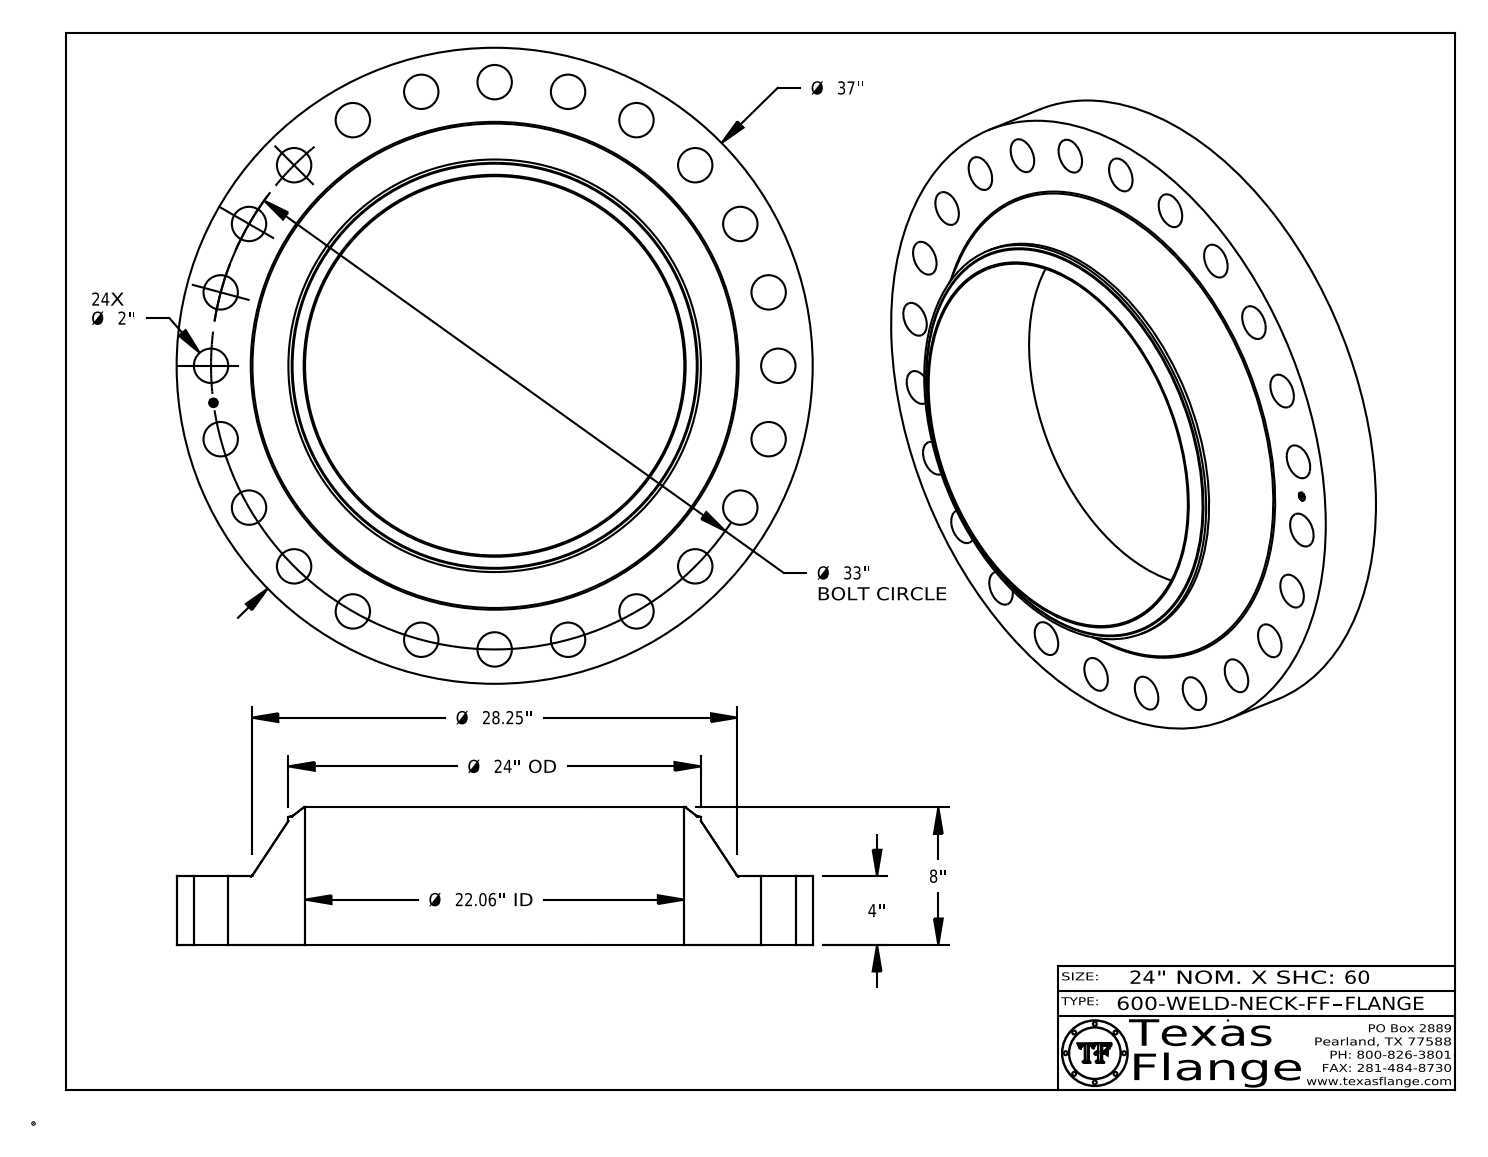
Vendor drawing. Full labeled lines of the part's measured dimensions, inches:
Part name (STEP PRODUCT): 600-WELD-NECK-FF
STEP written by: CATIA V5 STEP AP214 (AUTOMOTIVE_DESIGN)
Units: inches
Bodies: 1 solid, 452 faces (368 planar, 74 cylindrical, 10 other)
Overall size (bounding box): 37 × 37 × 8
Volume: 3 002 in³ · Surface area: 3 029 in²
Round holes (diameter × count): ⌀2 ×24, ⌀0.495 ×1, ⌀22.062 ×1
Round bosses / shafts (diameter × count): ⌀0.03 ×8, ⌀37 ×1, ⌀24 ×1, ⌀0.39 ×1
Main face-to-face distances: 4, 8, 0.015, 3.985, 4.015, 0.07, 0.148, 0.144, 0.027, 0.096
Hole centre spacings: 16.5, 4.307, 8.541, 20.089, 23.335, 26.181, 31.876, 32.718
